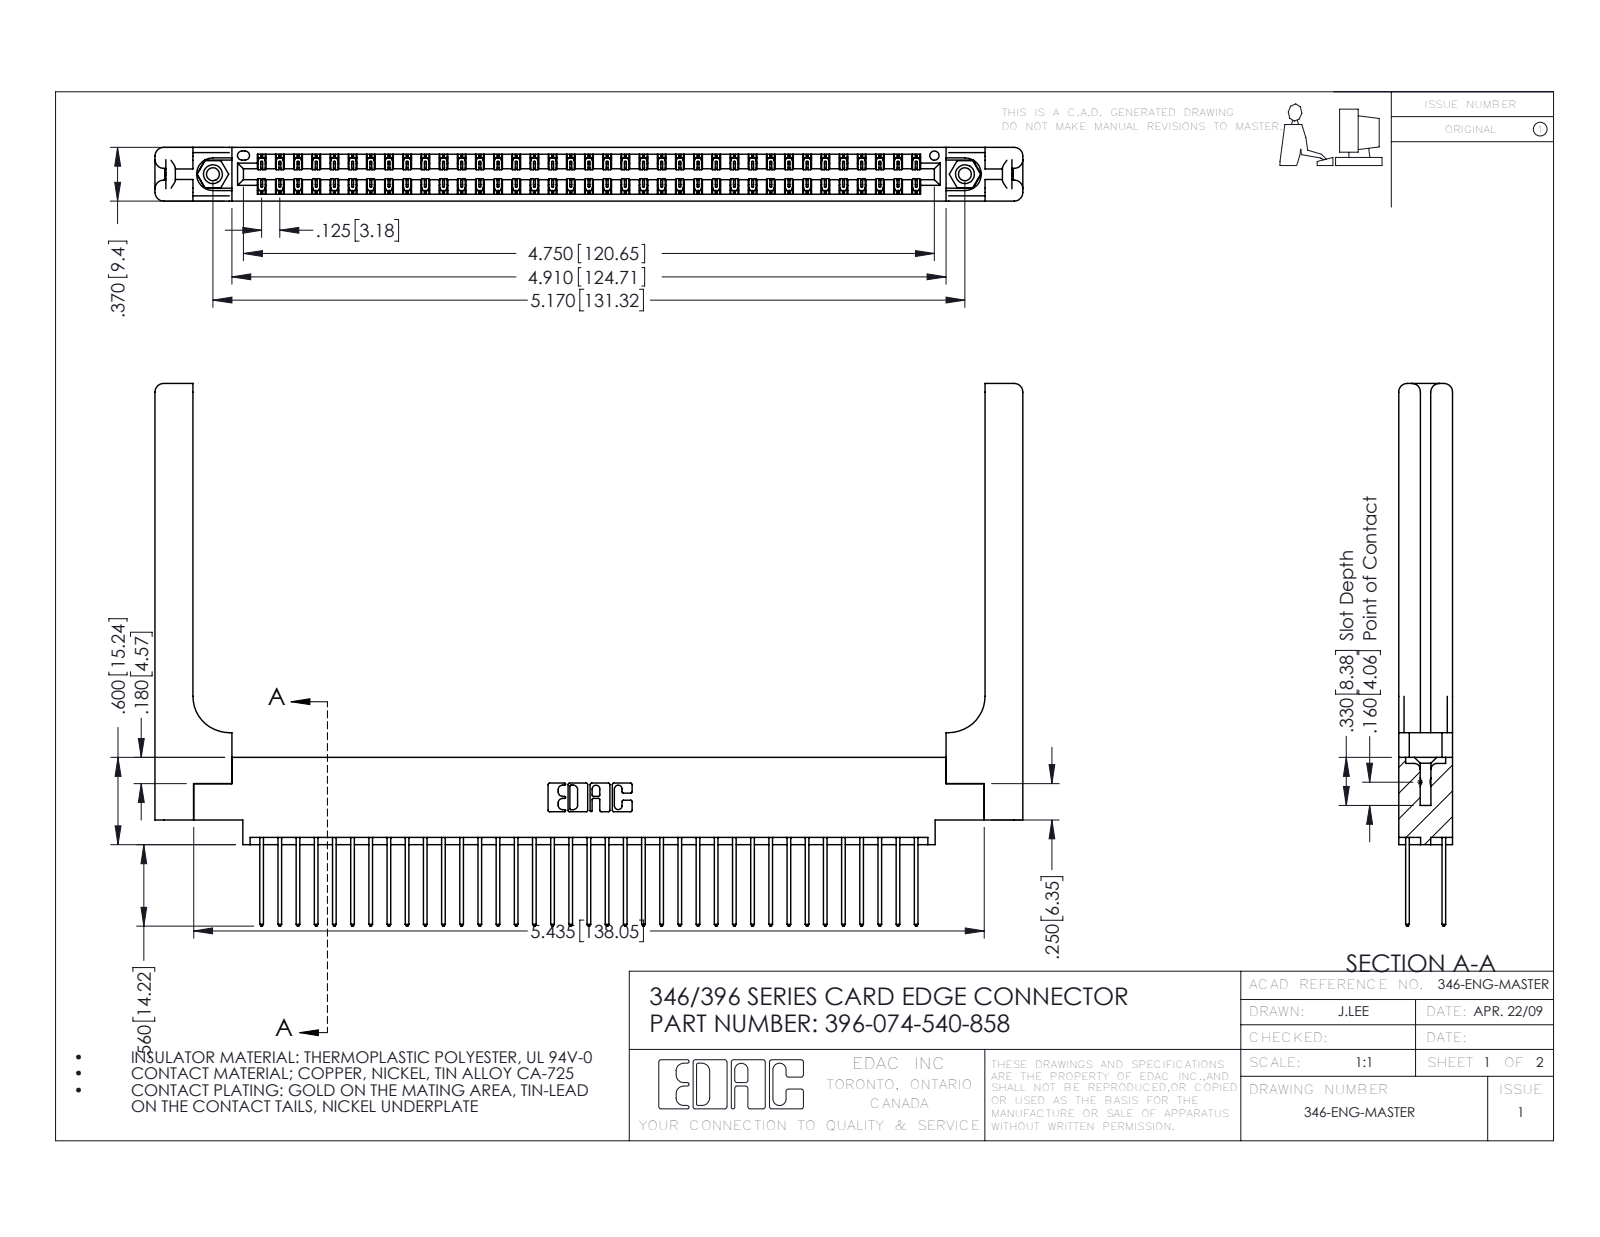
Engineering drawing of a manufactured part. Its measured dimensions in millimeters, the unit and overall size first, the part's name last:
Units: millimetres
Overall size (bounding box): 151.5 × 94.7 × 9.4
Round holes (diameter × count): ⌀2.3 ×2, ⌀3.2 ×2, ⌀4 ×2, ⌀1.6 ×1
Round bosses / shafts (diameter × count): ⌀3.9 ×2
Partial cylindrical surfaces — rounded edges, fillets, slot ends (radius × count): R0.2 ×111, R0.3 ×74, R0.3 ×22, R1.5 ×16, R0.2 ×6, R0.8 ×6, R0.7 ×3, R0.4 ×2
Main face-to-face distances: 1.2, 8.2, 9.4, 1.8, 6.4, 0.6, 7.6, 3.8, 3.8, 7
Hole centre spacings: 6.2, 126, 131.3
Volume: 22 350 mm³ · Surface area: 26 830 mm²
Bodies: 79 solids, 4230 faces (2818 planar, 1352 cylindrical, 60 other)
Part name (STEP PRODUCT): 345-250-001_345-250-001-102; 346-220-058_345-220-058; 346 Part_0.170 Offset - 0.156 Dia-TH; 345-292-001_345-293-140 (+1 more)
STEP written by: SolidWorks 2016 (CONFIG_CONTROL_DESIGN)
